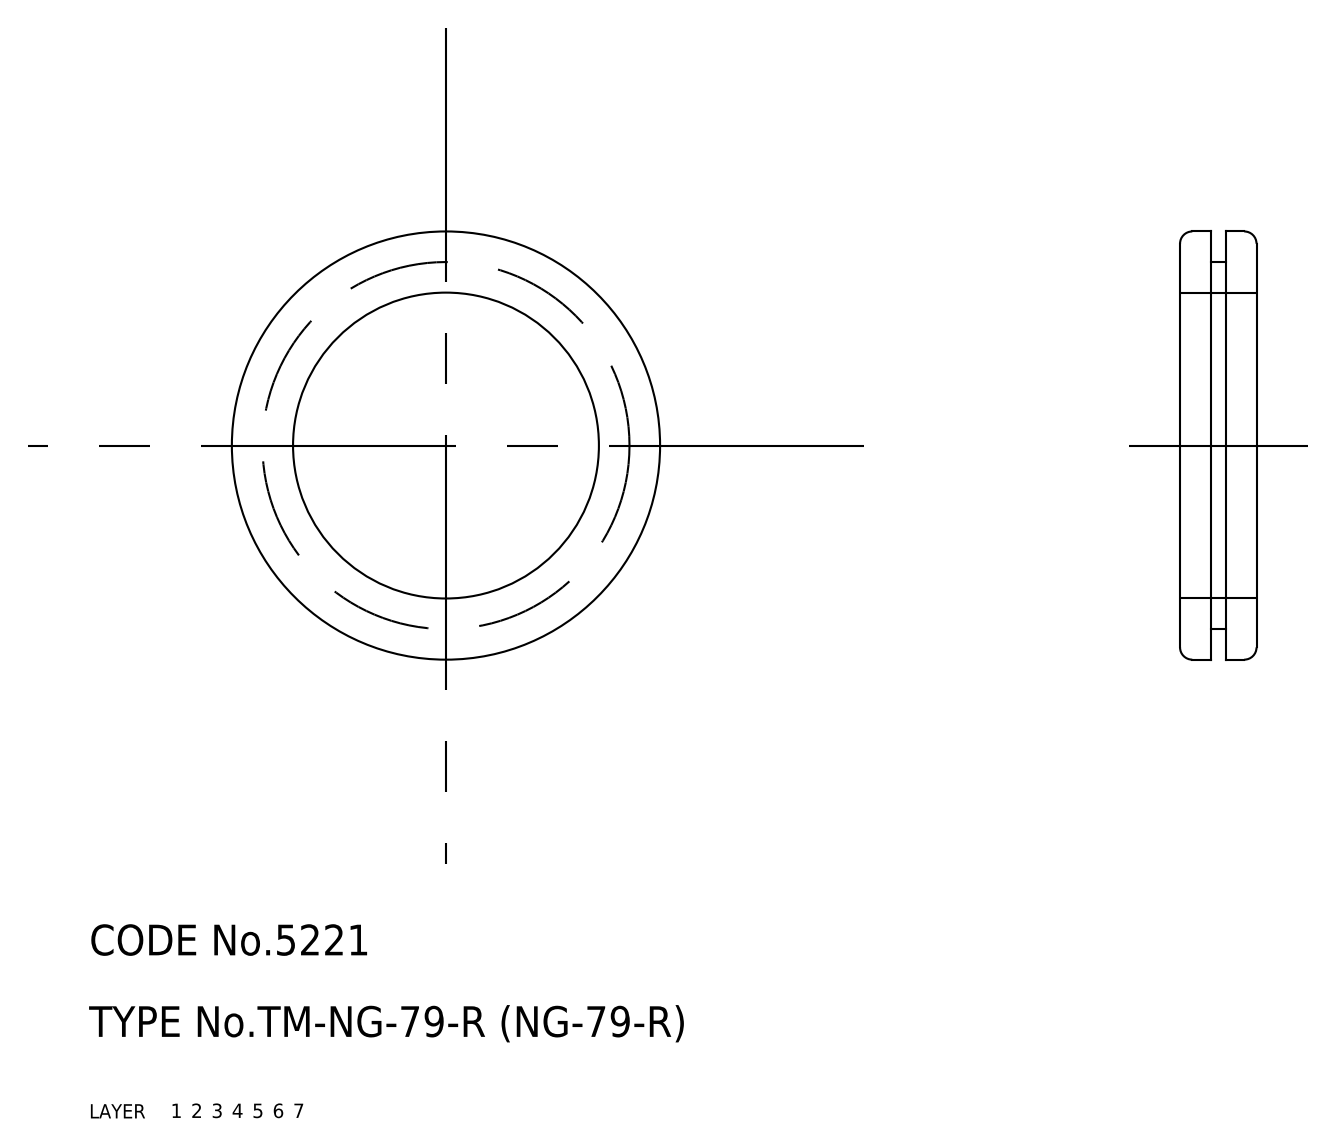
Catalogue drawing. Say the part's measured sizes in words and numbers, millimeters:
The part is named "grommet". Its 3-D file was written by "CADfix (AUTOMOTIVE_DESIGN)". It is 1 solid with 16 faces: 0 planar, 0 cylindrical and 16 other. Overall it measures 42 by 42 by 7.5 millimeters. Its volume is 4 477 cubic millimeters and its surface area 3 625 square millimeters.
